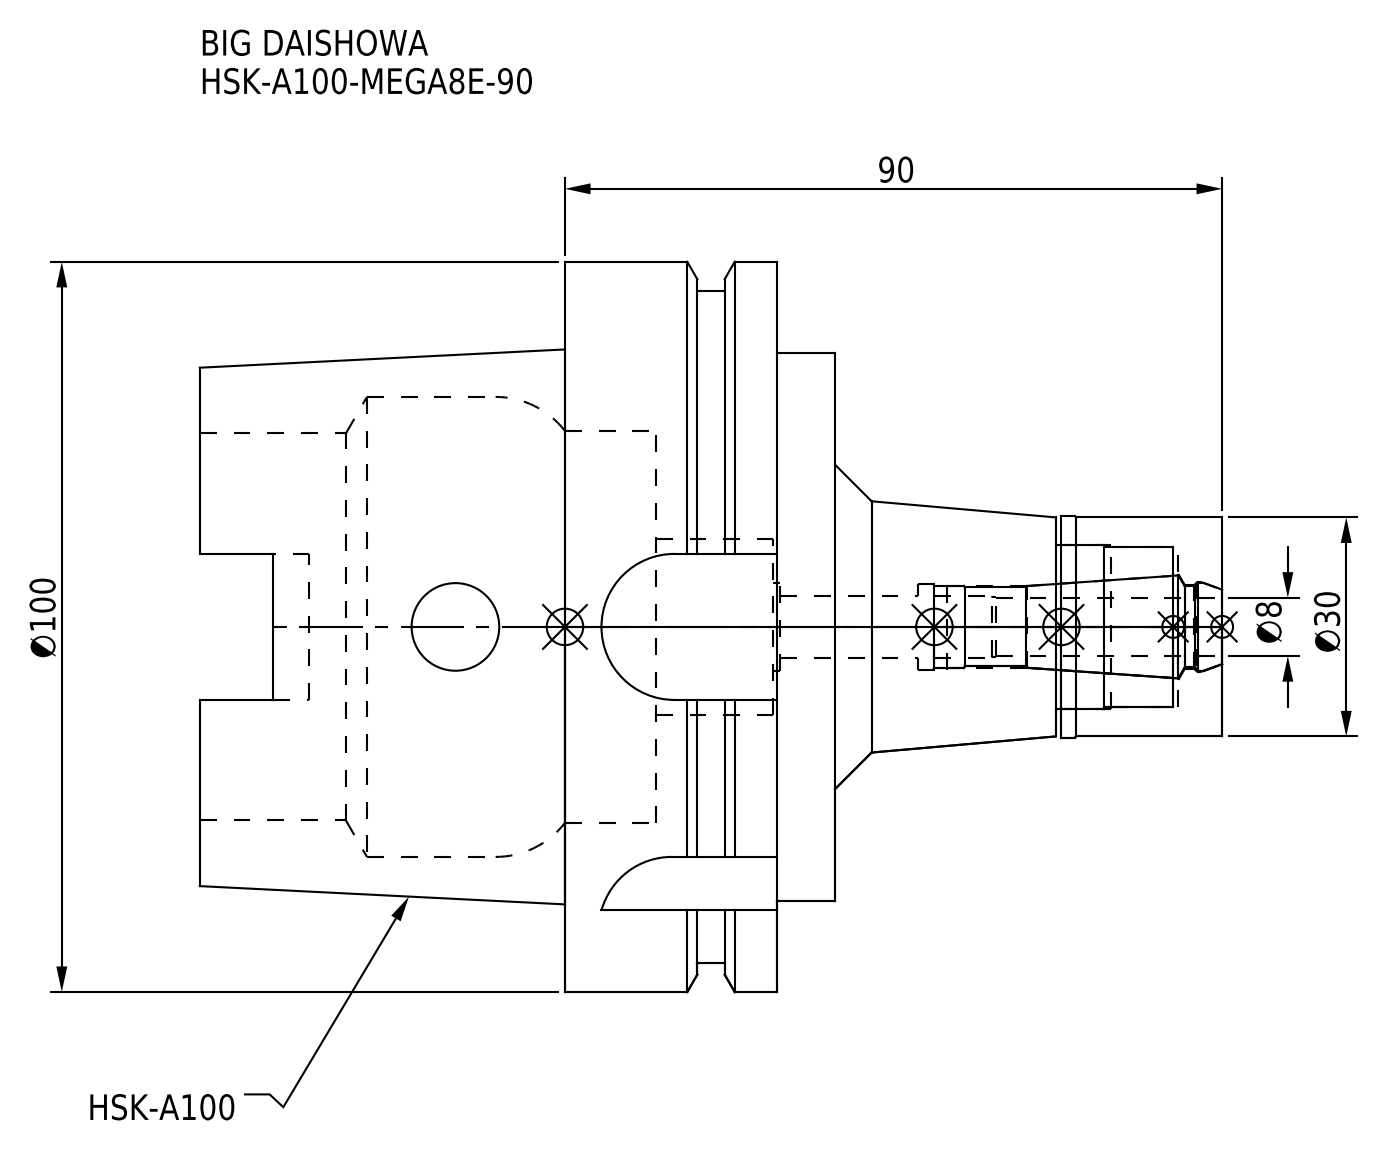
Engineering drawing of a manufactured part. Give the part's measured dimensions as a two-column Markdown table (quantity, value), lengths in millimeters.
| quantity | value |
| --- | --- |
| part name | MEN8_1.stp; HSK-A100-MEGA8E-90-080-FreeParts; HSK-A100-MEGA8E-90-080.stp; DXF_TEMP_ASSY_ASM_4_ASM.stp (+3 more) |
| STEP written by | SolidWorks 2019 (CONFIG_CONTROL_DESIGN) |
| units | millimeters |
| bodies | 2 solids, 126 faces (42 planar, 56 cylindrical, 28 other) |
| overall size | 140 × 100 × 100 |
| volume | 325 455 mm³ |
| surface area | 61 970 mm² |
| round holes (diameter × count) | 12 × 2, 8.4 × 1, 11.2 × 1, 11.4 × 1, 11.8 × 1, 12.3 × 1, 22 × 1, 22.5 × 1, 24 × 1, 53 × 1, 53.8 × 1, 63 × 1 |
| round bosses / shafts (diameter × count) | 100 × 1, 92 × 1, 75 × 1, 30.3 × 1, 30 × 1 |
| partial cylindrical surfaces (radius × count) | 4.88 × 4, 10 × 4 |
| main face-to-face distances | 29, 8, 37, 24.55, 16.55, 12.45, 79, 87, 62.45, 50 |
